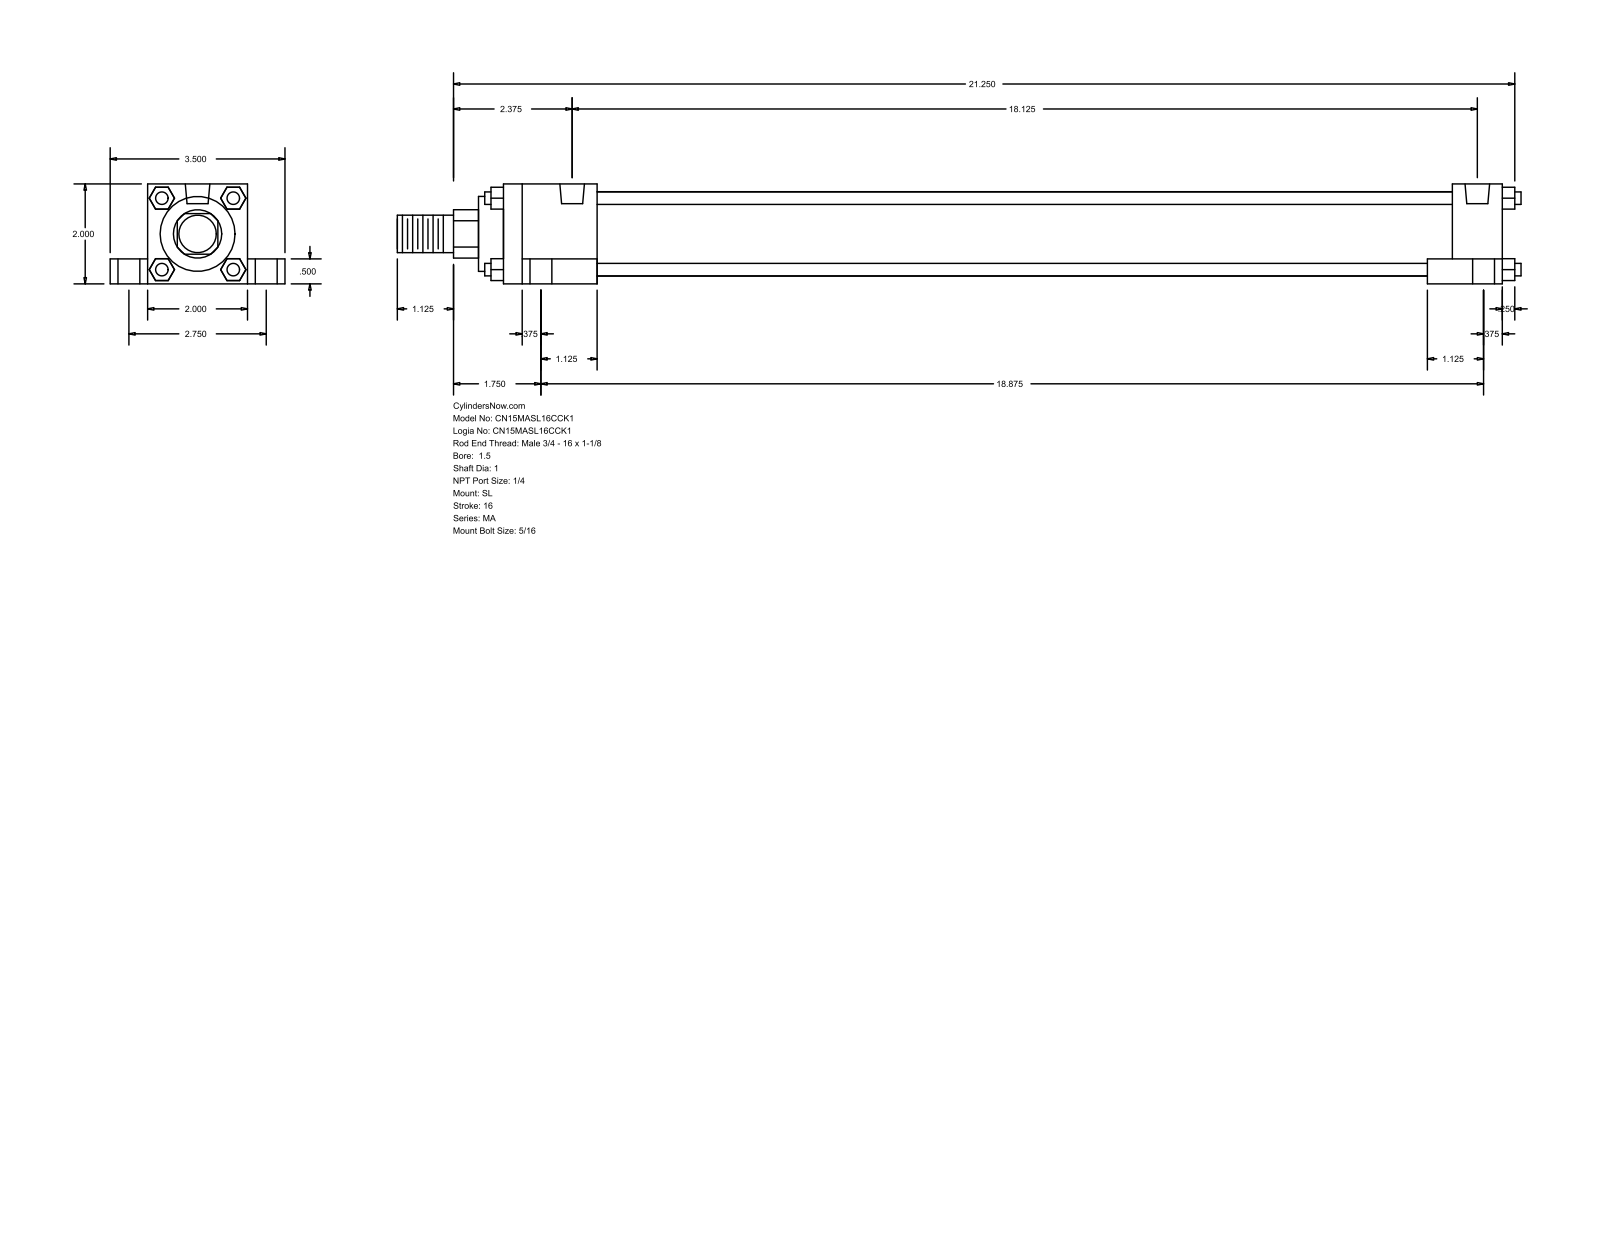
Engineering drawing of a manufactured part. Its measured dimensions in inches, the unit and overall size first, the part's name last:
Units: inches
Overall size (bounding box): 22.5 × 3.5 × 2
Round holes (diameter × count): ⌀0.313 ×4, ⌀0.437 ×4, ⌀0.687 ×4, ⌀0.492 ×2
Round bosses / shafts (diameter × count): ⌀0.25 ×4, ⌀1.69 ×1, ⌀1.5 ×1, ⌀1 ×1, ⌀0.75 ×1
Partial cylindrical surfaces — rounded edges, fillets, slot ends (radius × count): R0.484 ×1
Main face-to-face distances: 2, 0.5, 0.75, 2.75, 1.5, 0.375, 20, 1, 0.25, 19
Hole centre spacings: 1.38, 1.51, 2.75, 18.125, 18.302, 18.8, 18.875, 19.074
Bodies: 0 solids, 148 faces (112 planar, 36 cylindrical, 0 other)
Part name (STEP PRODUCT): MA_SL__0150_1
STEP written by: GSSL Pune (CONFIG_CONTROL_DESIGN)
